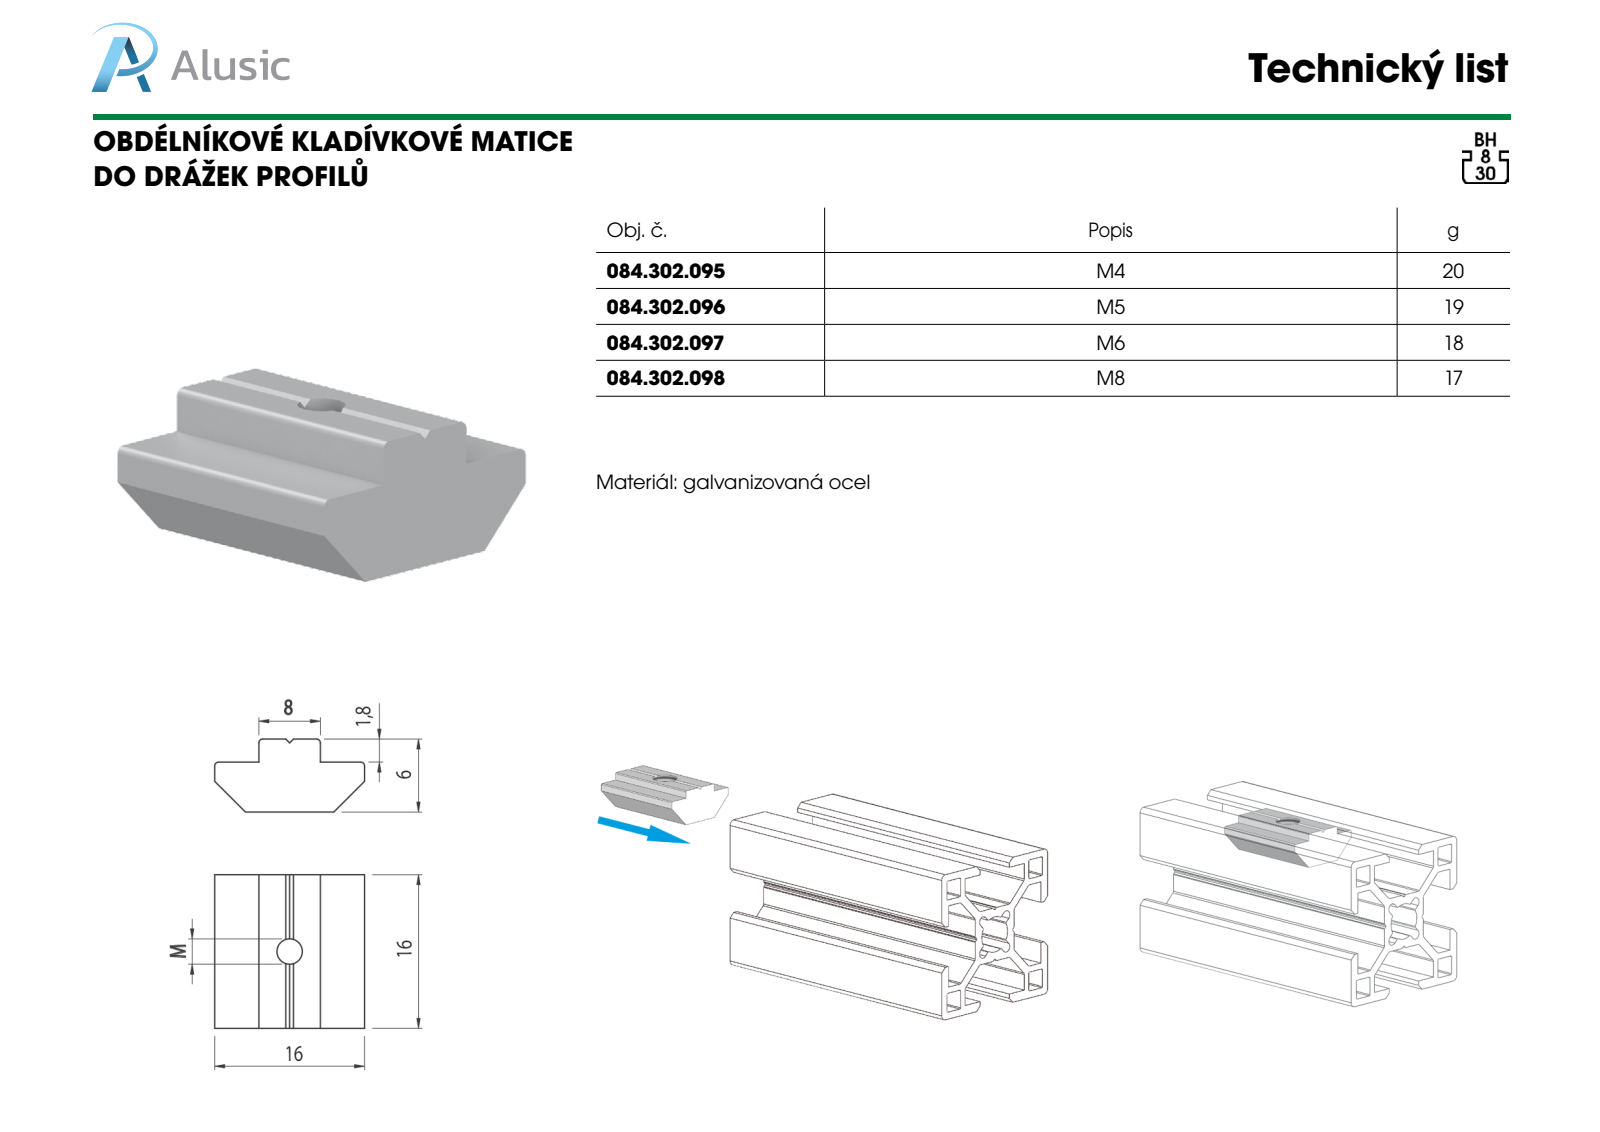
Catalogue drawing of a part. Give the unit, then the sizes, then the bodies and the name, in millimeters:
Units: millimetres
Overall size (bounding box): 20 × 19.5 × 9.5
Round holes (diameter × count): ⌀3.3 ×1
Partial cylindrical surfaces — rounded edges, fillets, slot ends (radius × count): R0.5 ×4
Main face-to-face distances: 6.5, 20, 9.5, 3, 5.75, 13.75, 8, 19.5, 10.43
Volume: 2 605 mm³ · Surface area: 1 405 mm²
Bodies: 1 solid, 23 faces (17 planar, 6 cylindrical, 0 other)
Part name (STEP PRODUCT): 3.NUT.020
STEP written by: SolidWorks 2012 (CONFIG_CONTROL_DESIGN)
